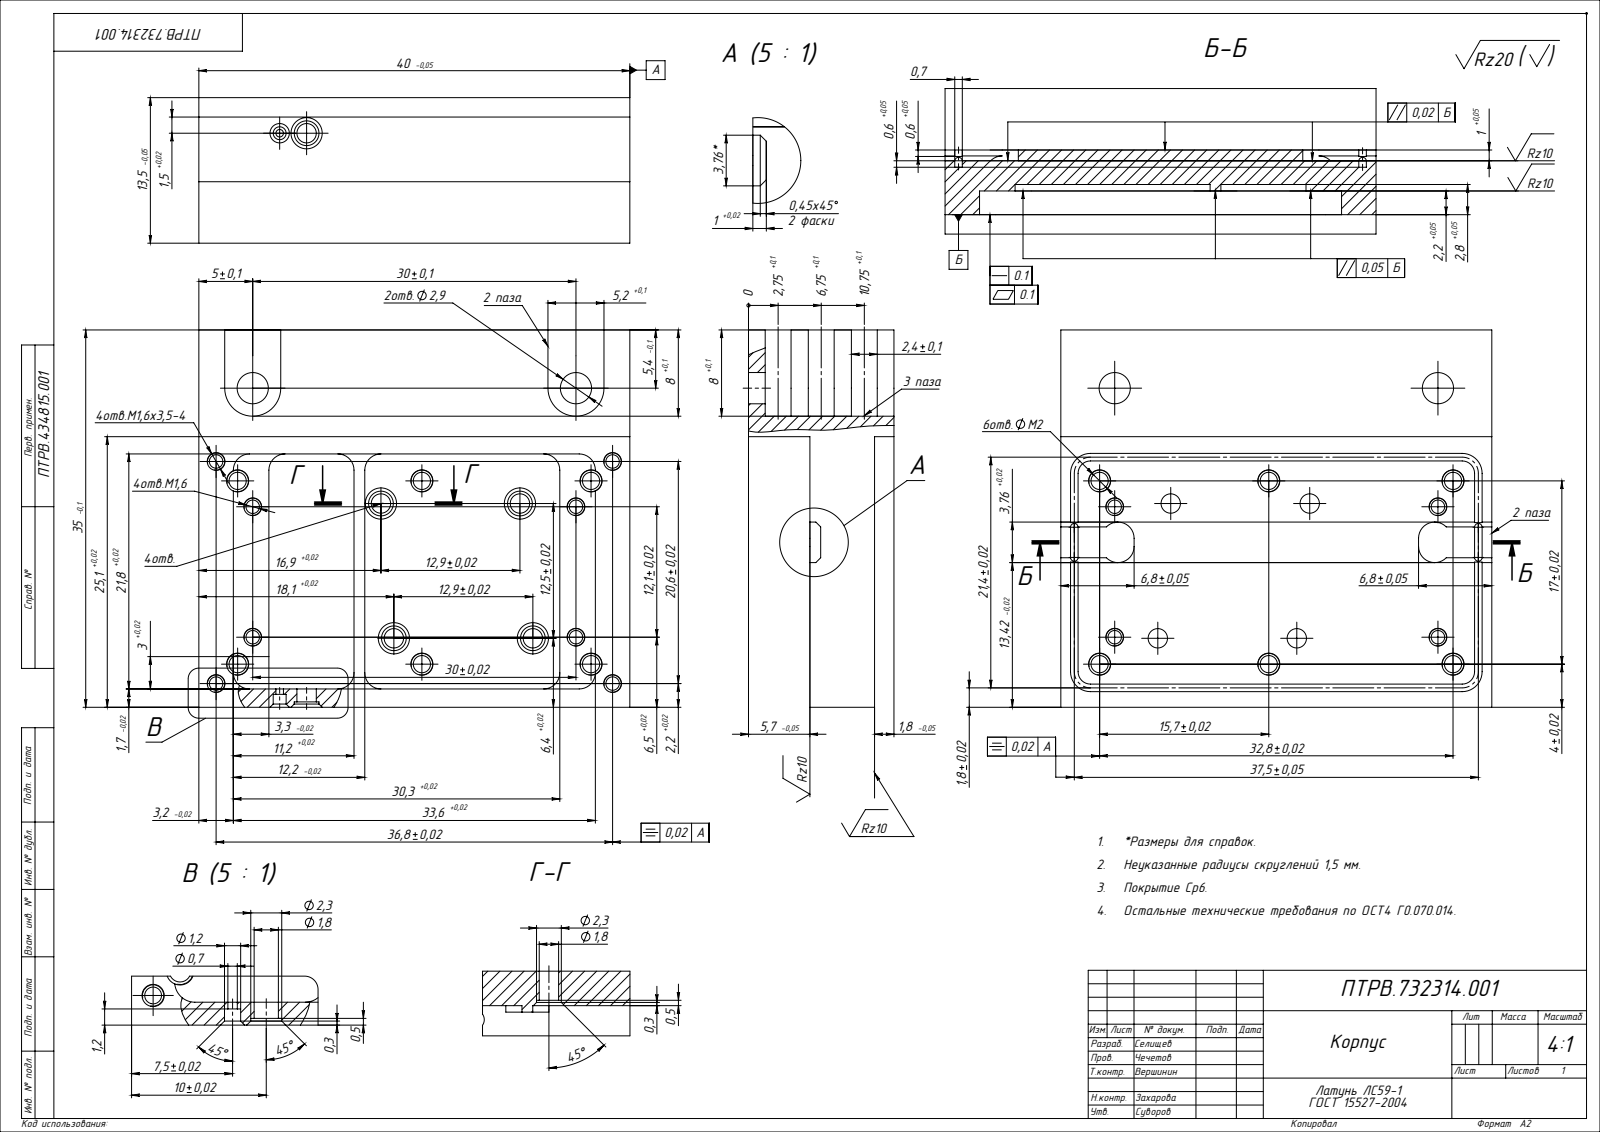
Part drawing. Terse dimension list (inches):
name: ПТРВ.732314.001 Корпус
written by: SolidWorks 2018 (CONFIG_CONTROL_DESIGN)
unit: in
bodies: 1 solid, 212 faces (112 planar, 66 cylindrical, 34 other)
size: 1.575 × 1.378 × 0.531
volume: 0.396 in³; area: 10.31 in²
holes: 8× ⌀0.049, 6× ⌀0.063, 5× ⌀0.071, 5× ⌀0.091, 2× ⌀0.114, 1× ⌀0.028, 1× ⌀0.047
rounds: 15× R0.059, 4× R0.014, 4× R0.04, 4× R0.045, 4× R0.073, 2× R0.102
face distances: 0.157, 0.094, 0.061, 0.315, 0.126, 0.156, 0.219, 0.313, 0.063, 0.47
hole spacings: 1.372, 0.106, 0.744, 1.557, 0.669, 1.181, 1.325, 0.109
